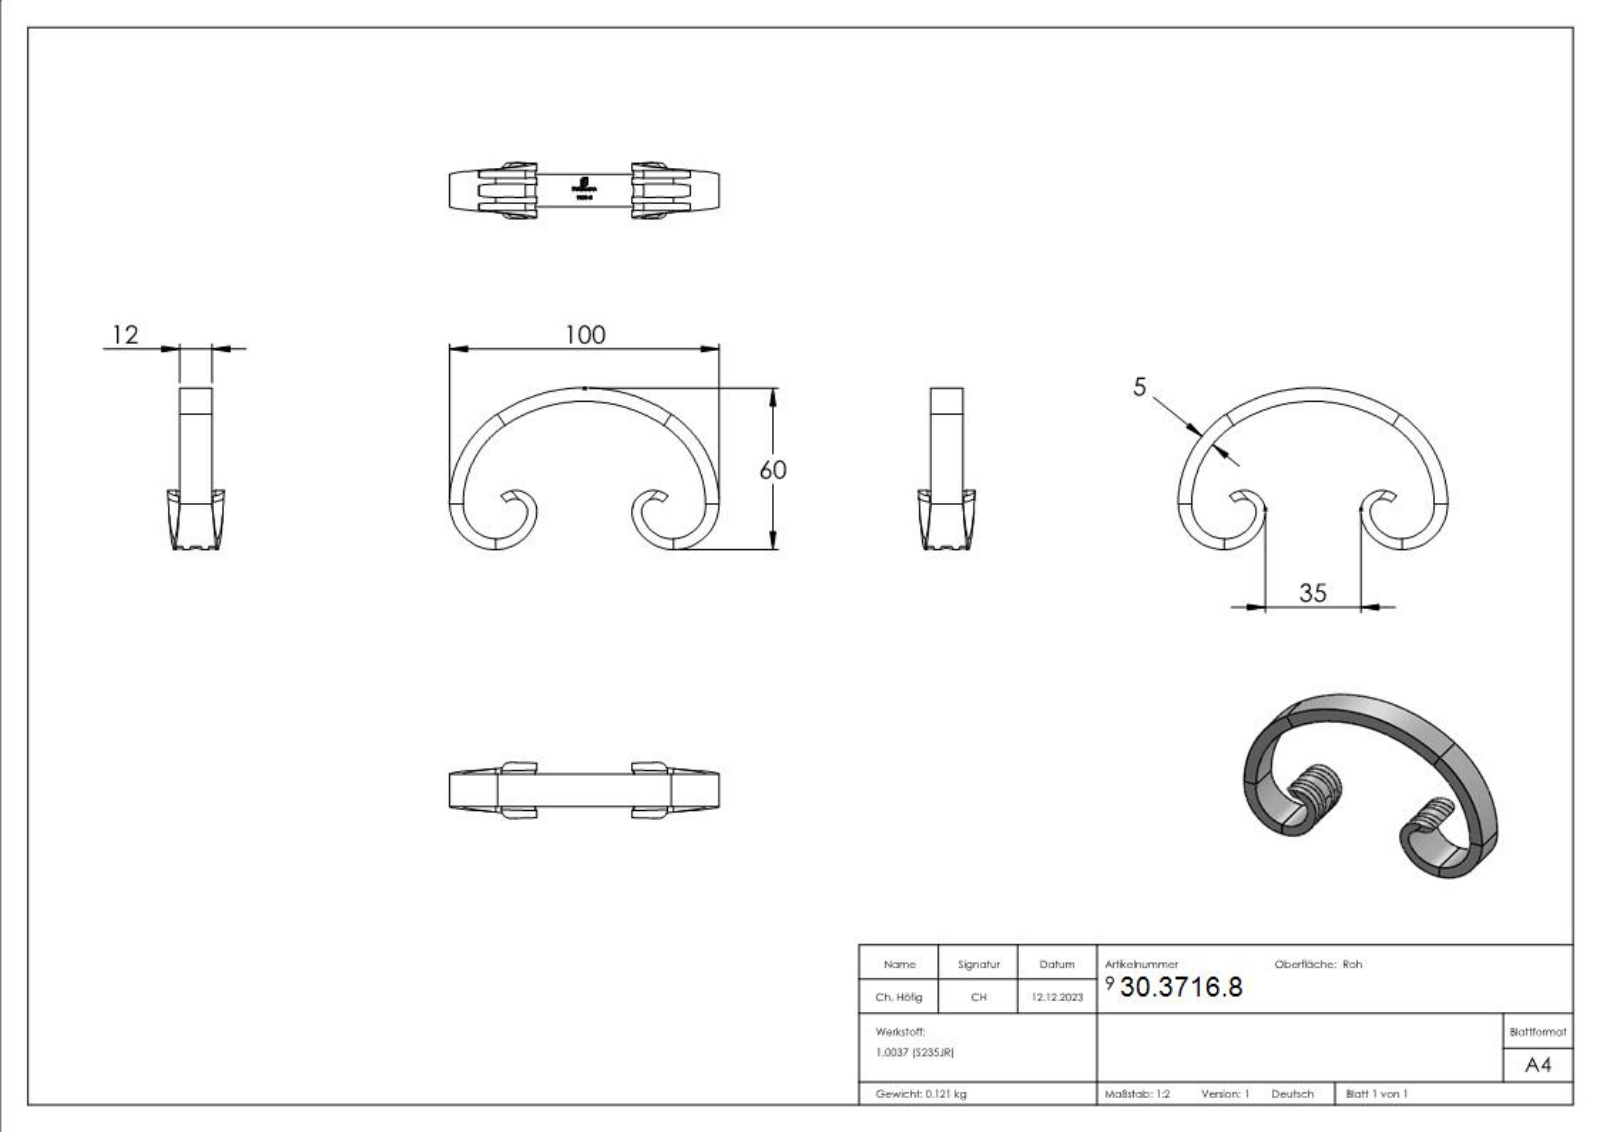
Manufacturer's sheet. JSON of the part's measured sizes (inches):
{"part_name": "9001-S", "step_written_by": "SolidWorks 2018 (CONFIG_CONTROL_DESIGN)", "units": "inches", "bodies": {"solids": 1, "faces": 286, "planar": 105, "cylindrical": 27, "other": 154}, "overall_size": [3.937, 2.362, 0.819], "volume_in3": 0.946, "surface_area_in2": 15.06, "partial_cylinders_radius": [[1.378, 2], [1.575, 2], [2.087, 1], [2.091, 1], [2.283, 1]], "face_to_face_distances": [0.472, 0.072, 0.045, 0.068, 0.117, 0.077, 0.049, 0.054, 0.133, 0.013]}
